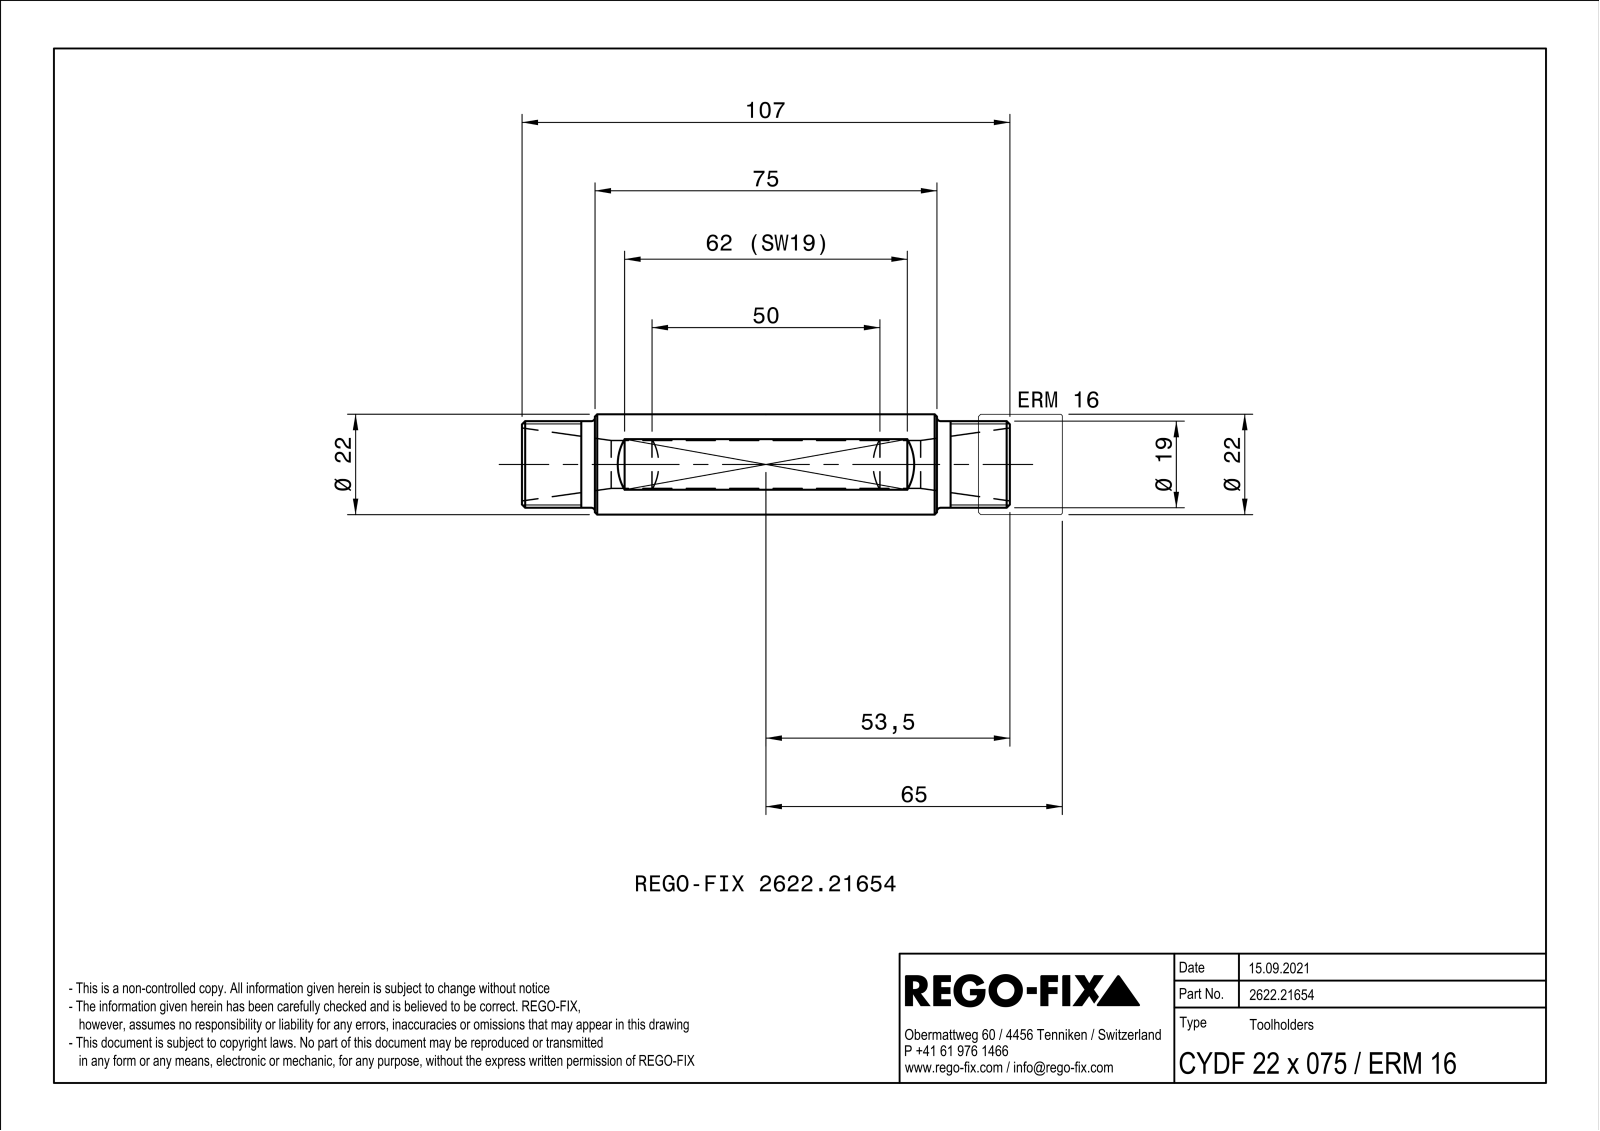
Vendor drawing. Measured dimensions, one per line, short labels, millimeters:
name: NOCUT
written by: SIEMENS PLM Software Solid Edge ST10 (AUTOMOTIVE_DESIGN)
unit: mm
bodies: 1 solid, 29 faces (13 planar, 6 cylindrical, 10 other)
size: 107 × 22 × 22
volume: 25 329 mm³; area: 11 182 mm²
holes: 1× ⌀10.5
bosses: 1× ⌀22, 1× ⌀19
face distances: 19, 107, 30.4, 9.19, 39.59, 16, 91, 75
